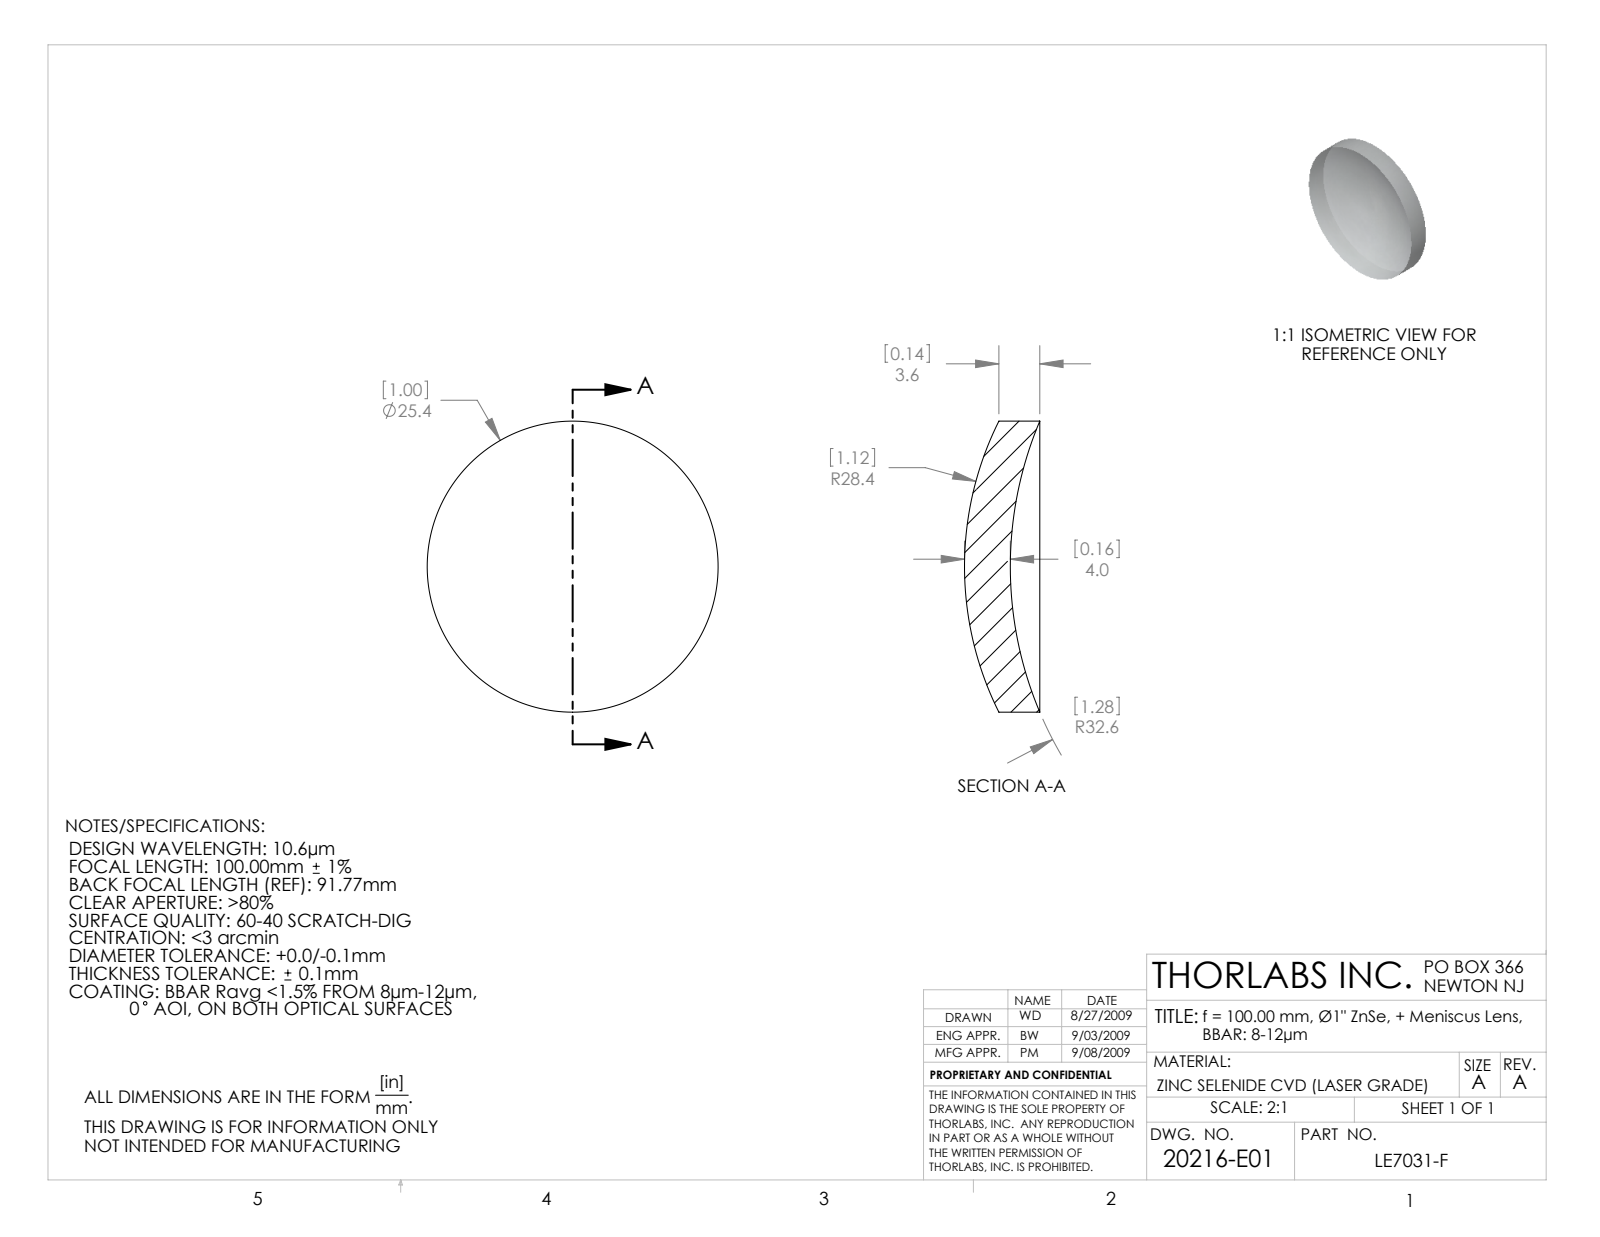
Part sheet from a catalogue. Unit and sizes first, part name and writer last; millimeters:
Units: millimetres
Overall size (bounding box): 25.4 × 25.4 × 6.57
Round bosses / shafts (diameter × count): ⌀25.4 ×1
Volume: 1 923 mm³ · Surface area: 1 348 mm²
Bodies: 1 solid, 6 faces (0 planar, 2 cylindrical, 4 other)
Part name (STEP PRODUCT): 20216-E0W
STEP written by: SolidWorks 2007 (CONFIG_CONTROL_DESIGN)
